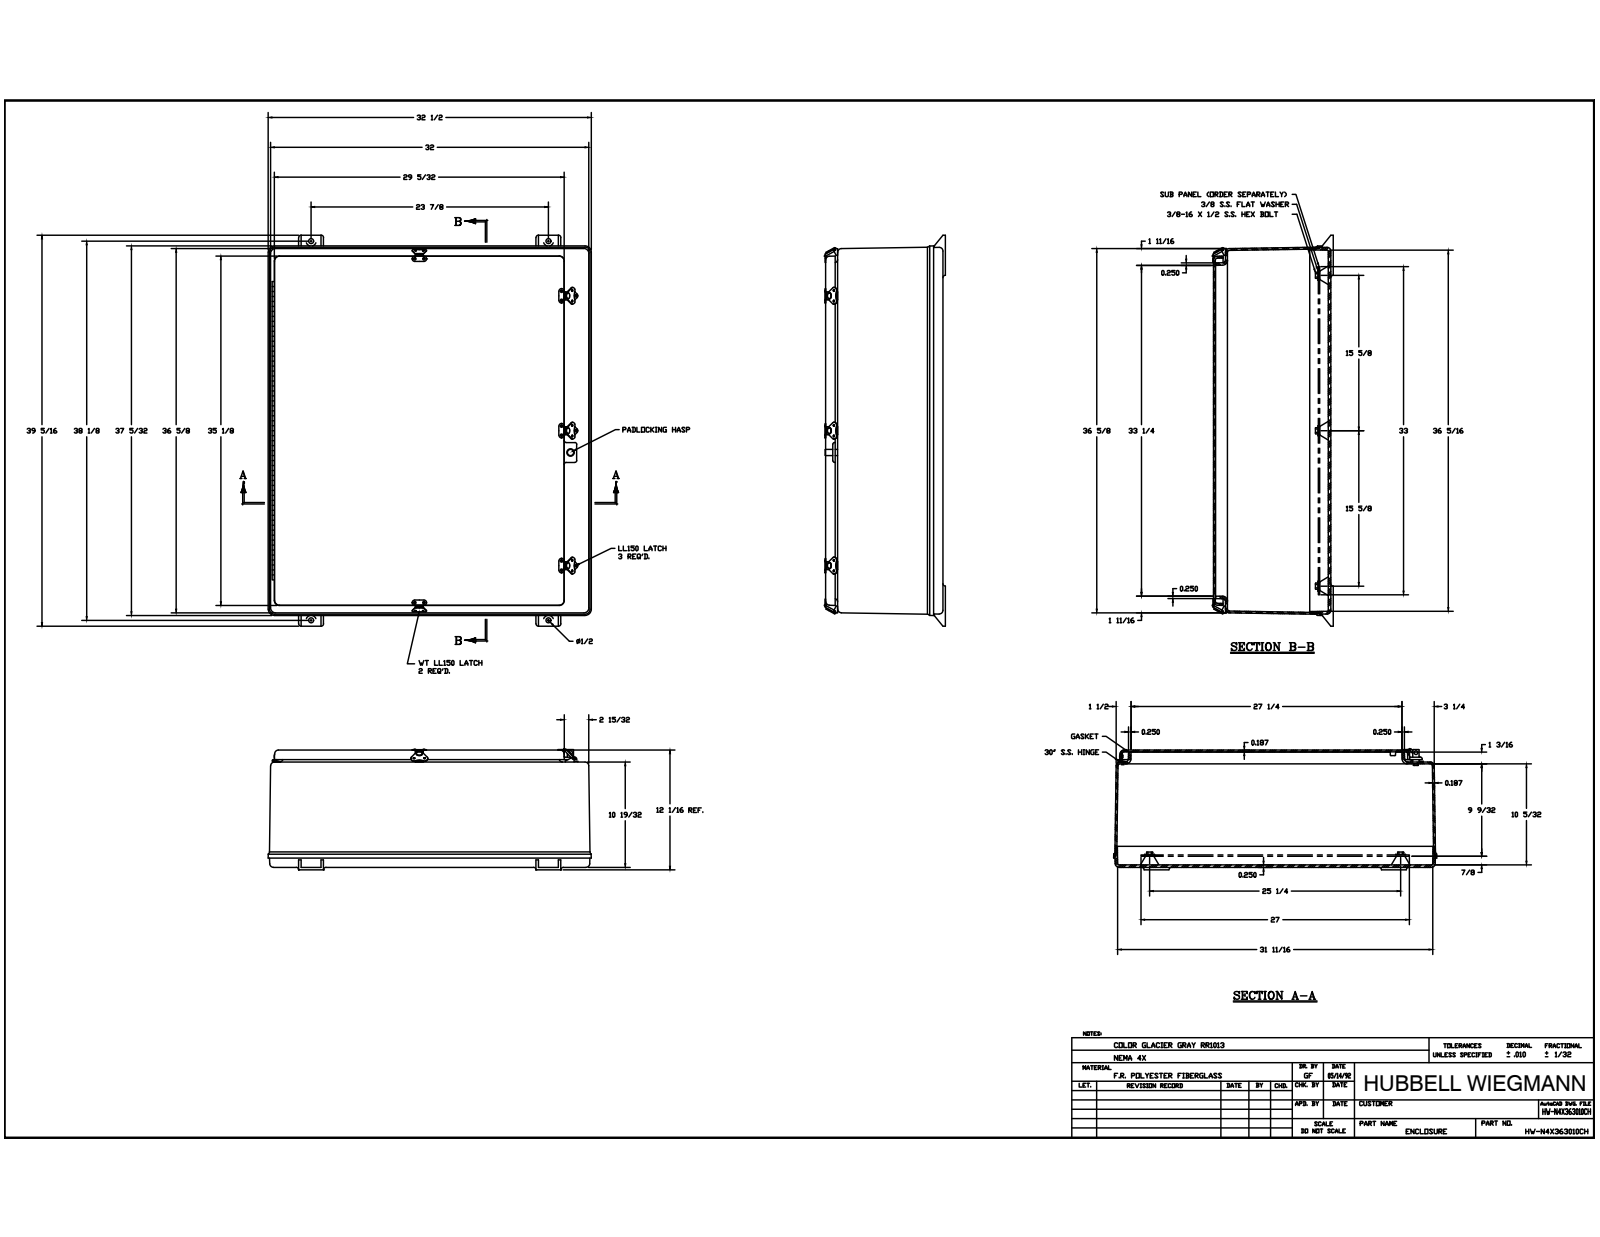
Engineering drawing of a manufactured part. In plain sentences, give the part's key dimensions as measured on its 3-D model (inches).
The part is named "WPN363010SHWT; WPN3630B; WPN363010HWTPCVR; N363010G (+8 more)". Its 3-D file was written by "Autodesk Inventor 2014 (AUTOMOTIVE_DESIGN)". It is 63 solids with 1832 faces: 704 planar, 736 cylindrical and 392 other. Overall it measures 39.313 by 32.5 by 12.397 inches. Its volume is 875.7 cubic inches and its surface area 8 812 square inches. Round holes: 36 of diameter 0.13, 20 of diameter 0.063, 10 of diameter 0.138, 10 of diameter 0.187, 8 of diameter 0.065, 4 of diameter 0.563, 3 of diameter 0.135, 3 of diameter 0.156, 2 of diameter 0.433, 2 of diameter 0.51, 2 of diameter 0.51, 1 of diameter 0.125. Round bosses or shafts: 20 of diameter 0.14, 8 of diameter 0.297, 5 of diameter 0.5, 3 of diameter 0.2, 1 of diameter 0.25, 1 of diameter 0.201, 1 of diameter 0.135. Partial cylindrical surfaces (rounded edges, fillets, slot ends): 127 of radius 0.01, 24 of radius 0.25, 23 of radius 0.313, 21 of radius 0.187, 20 of radius 0.03, 13 of radius 0.375, 12 of radius 0.5, 10 of radius 0.063. The main face-to-face distances are 0.25, 11.813, 11.563, 11.624, 11.374, 0.188, 0.187, 0.188, 10.594, 1.219. The hole center spacings are 9.5, 19.5, 13.563, 1, 10, 29, 3.474, 3.785.
